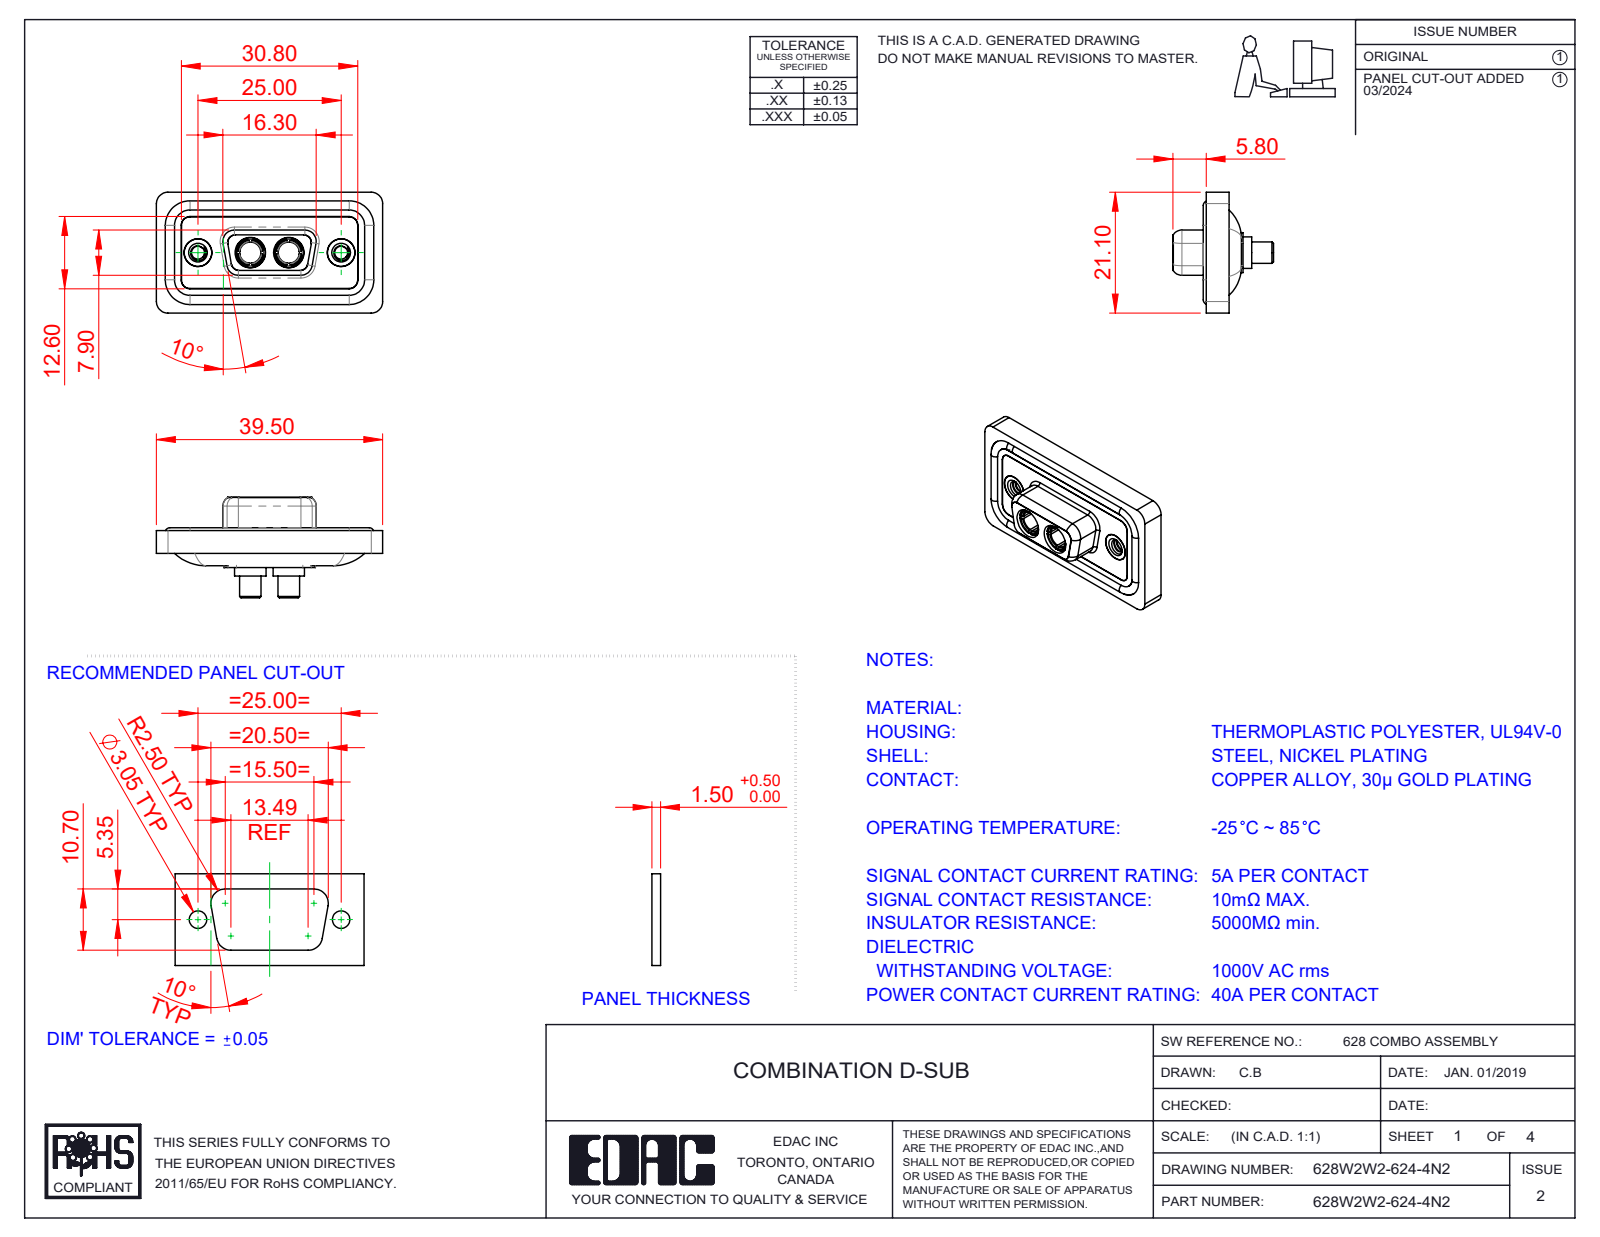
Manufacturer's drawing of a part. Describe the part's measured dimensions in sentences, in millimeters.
The part is named "628Combo Shell Front_09 Contacts; 628Combo Threaded Rivet_2; 628Combo Shell Rear_09 Contacts; 628Combo Housing_2W2 (+3 more)". Its 3-D file was written by "SolidWorks 2023 (CONFIG_CONTROL_DESIGN)". It is 11 solids with 534 faces: 163 planar, 234 cylindrical and 137 other. Overall it measures 39.5 by 21.1 by 17.55 millimeters. Its volume is 4 750 cubic millimeters and its surface area 7 658 square millimeters. Round holes: 4 of diameter 4.85, 2 of diameter 2.26, 2 of diameter 3.7, 2 of diameter 4, 2 of diameter 4.05, 2 of diameter 5, 2 of diameter 5.3. Round bosses or shafts: 4 of diameter 1.6, 2 of diameter 5.5, 2 of diameter 5.2, 2 of diameter 4.96, 2 of diameter 4.95, 2 of diameter 4.8, 2 of diameter 4.75, 2 of diameter 3.75. Partial cylindrical surfaces (rounded edges, fillets, slot ends): 22 of radius 1.5, 18 of radius 2, 8 of radius 1.35, 8 of radius 1.6, 4 of radius 0.25, 4 of radius 0.5, 4 of radius 0.6, 4 of radius 0.65. The main face-to-face distances are 0.4, 1.8, 1.1, 2.9, 0.5, 1.6, 5.65, 7.45, 5.35, 3.1. The hole center spacings are 9.14, 15.86, 6.72, 25.
